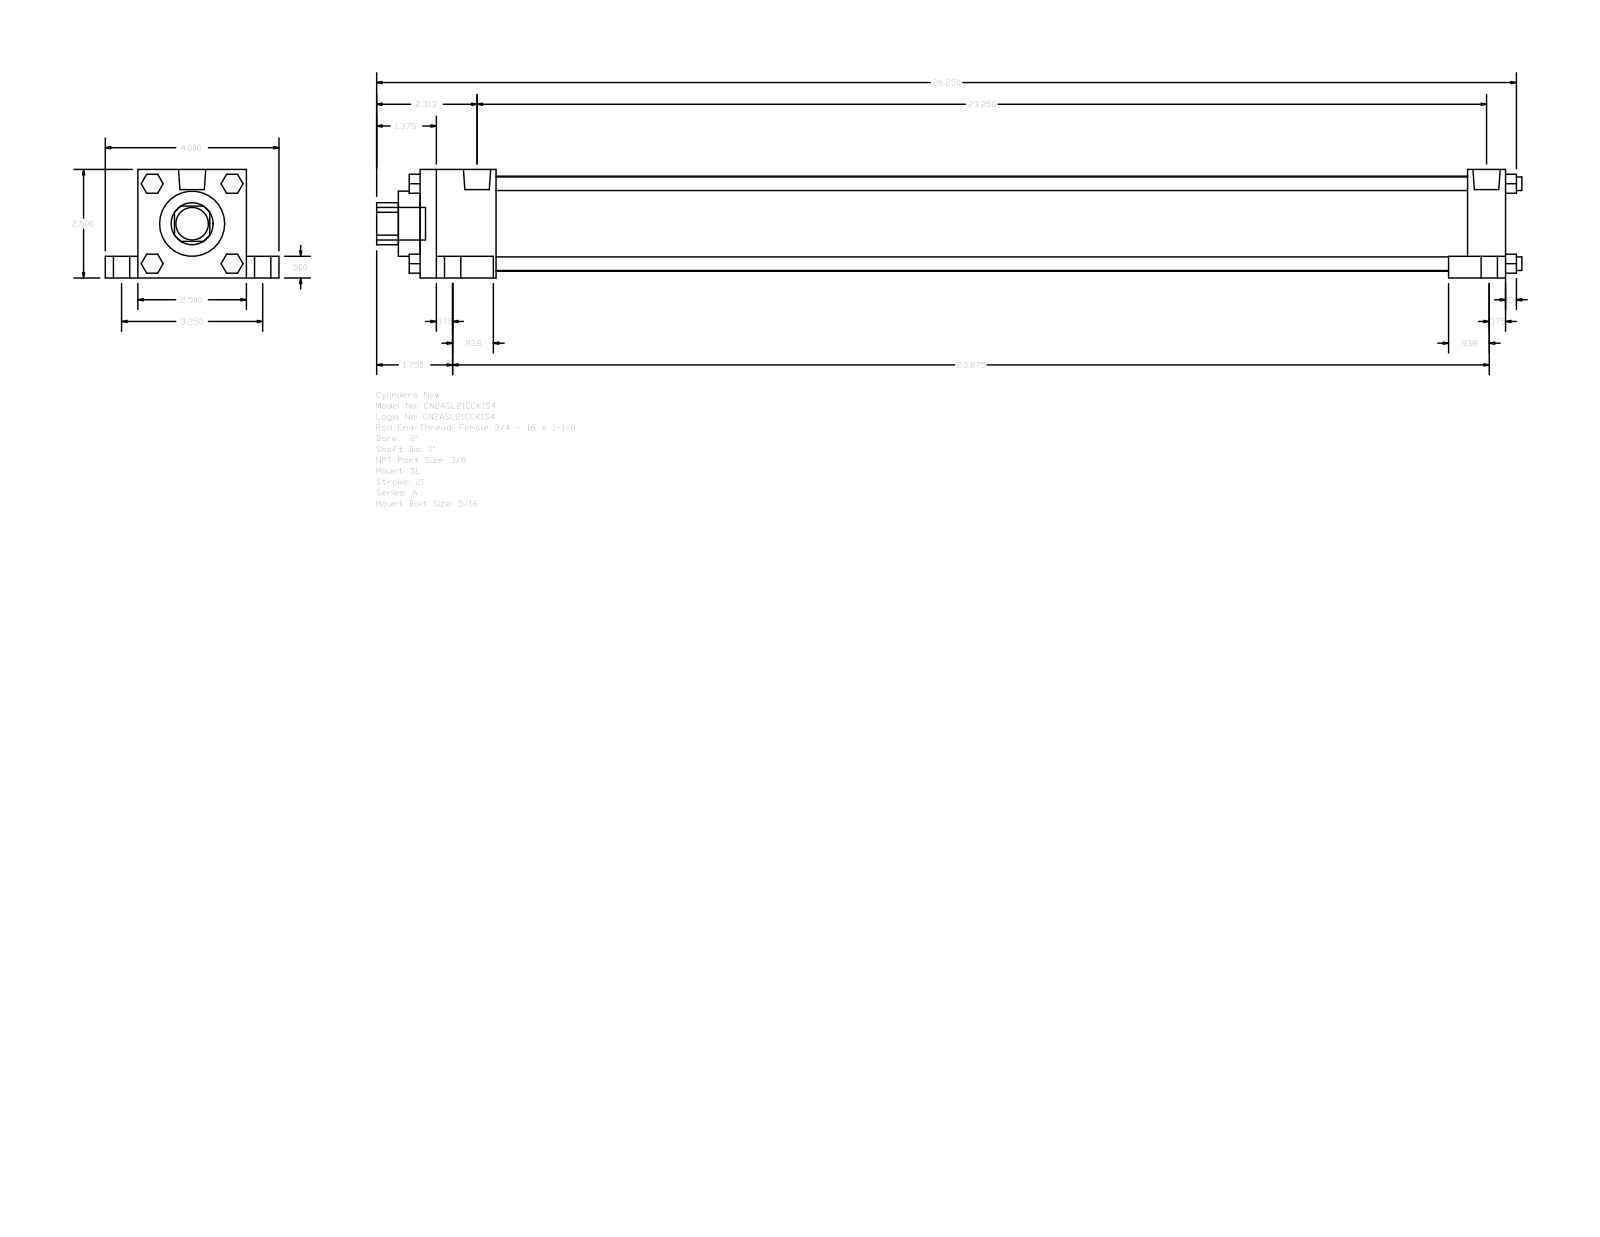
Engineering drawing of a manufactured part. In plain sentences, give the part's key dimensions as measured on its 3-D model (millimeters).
The part is named "A_SL__0200_1". Its 3-D file was written by "GSSL Pune (CONFIG_CONTROL_DESIGN)". It is 0 solids with 148 faces: 112 planar, 36 cylindrical and 0 other. Overall it measures 669.92 by 101.6 by 63.5 millimeters. Round holes: 1 of diameter 25.4, 1 of diameter 38.1, 1 of diameter 55.63. Round bosses or shafts: 4 of diameter 15.88, 4 of diameter 9.53, 4 of diameter 7.94, 4 of diameter 5.56, 2 of diameter 15.93, 1 of diameter 19.05. Partial cylindrical surfaces (rounded edges, fillets, slot ends): 1 of radius 12.29. The main face-to-face distances are 63.5, 635, 12.7, 50.8, 19.05, 82.55, 9.52, 44.45, 590.55, 612.77.
